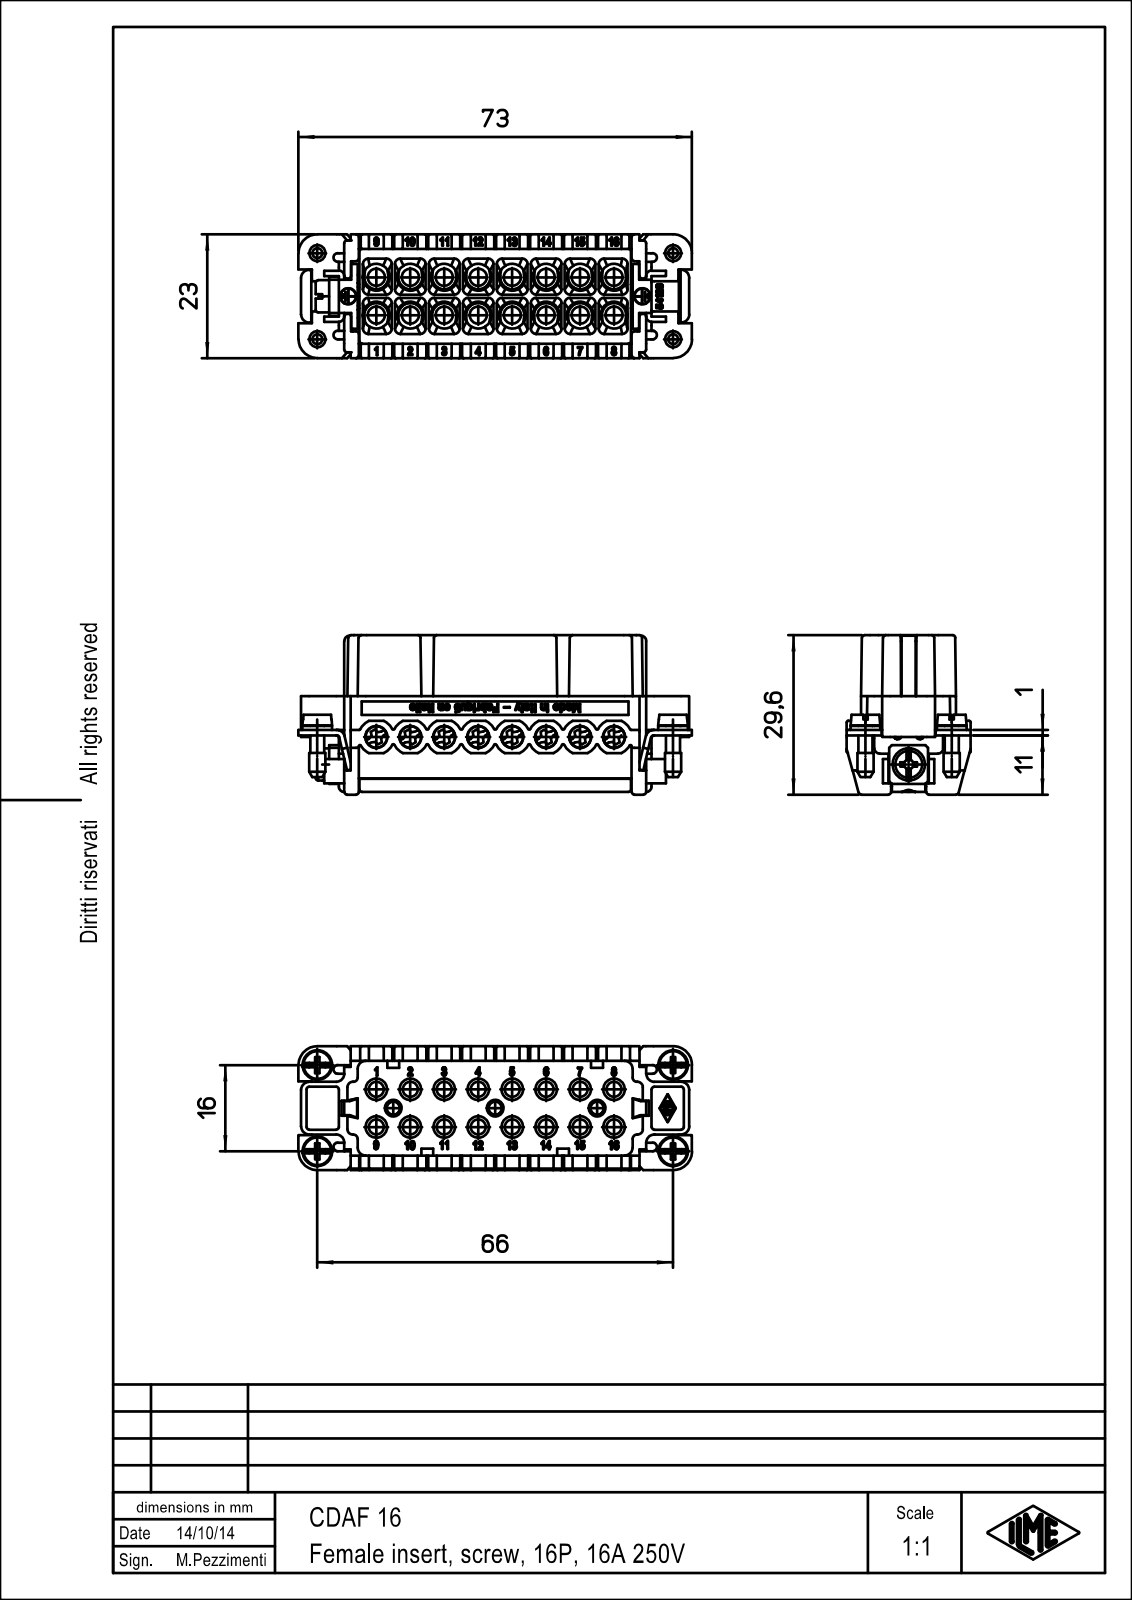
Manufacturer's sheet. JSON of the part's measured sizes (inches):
{"part_name": "CDAF_16", "step_written_by": "PTC Creo Elements/Direct Modeling 19.0E 27-Jun-2016 (C) Parametric Technology GmbH (AUTOMOTIVE_DESIGN)", "units": "inches", "bodies": {"solids": 22, "faces": 2794, "planar": 2414, "cylindrical": 34, "other": 346}, "overall_size": [2.089, 0.906, 0.39], "volume_in3": 0.003, "surface_area_in2": 3.441, "round_holes": [[0.138, 1]], "round_bosses_or_shafts": [[0.157, 8]], "face_to_face_distances": [0.031, 0.874, 0.028, 0.878, 0.846, 0.906, 0.124, 0.843, 0.85, 0.248]}
